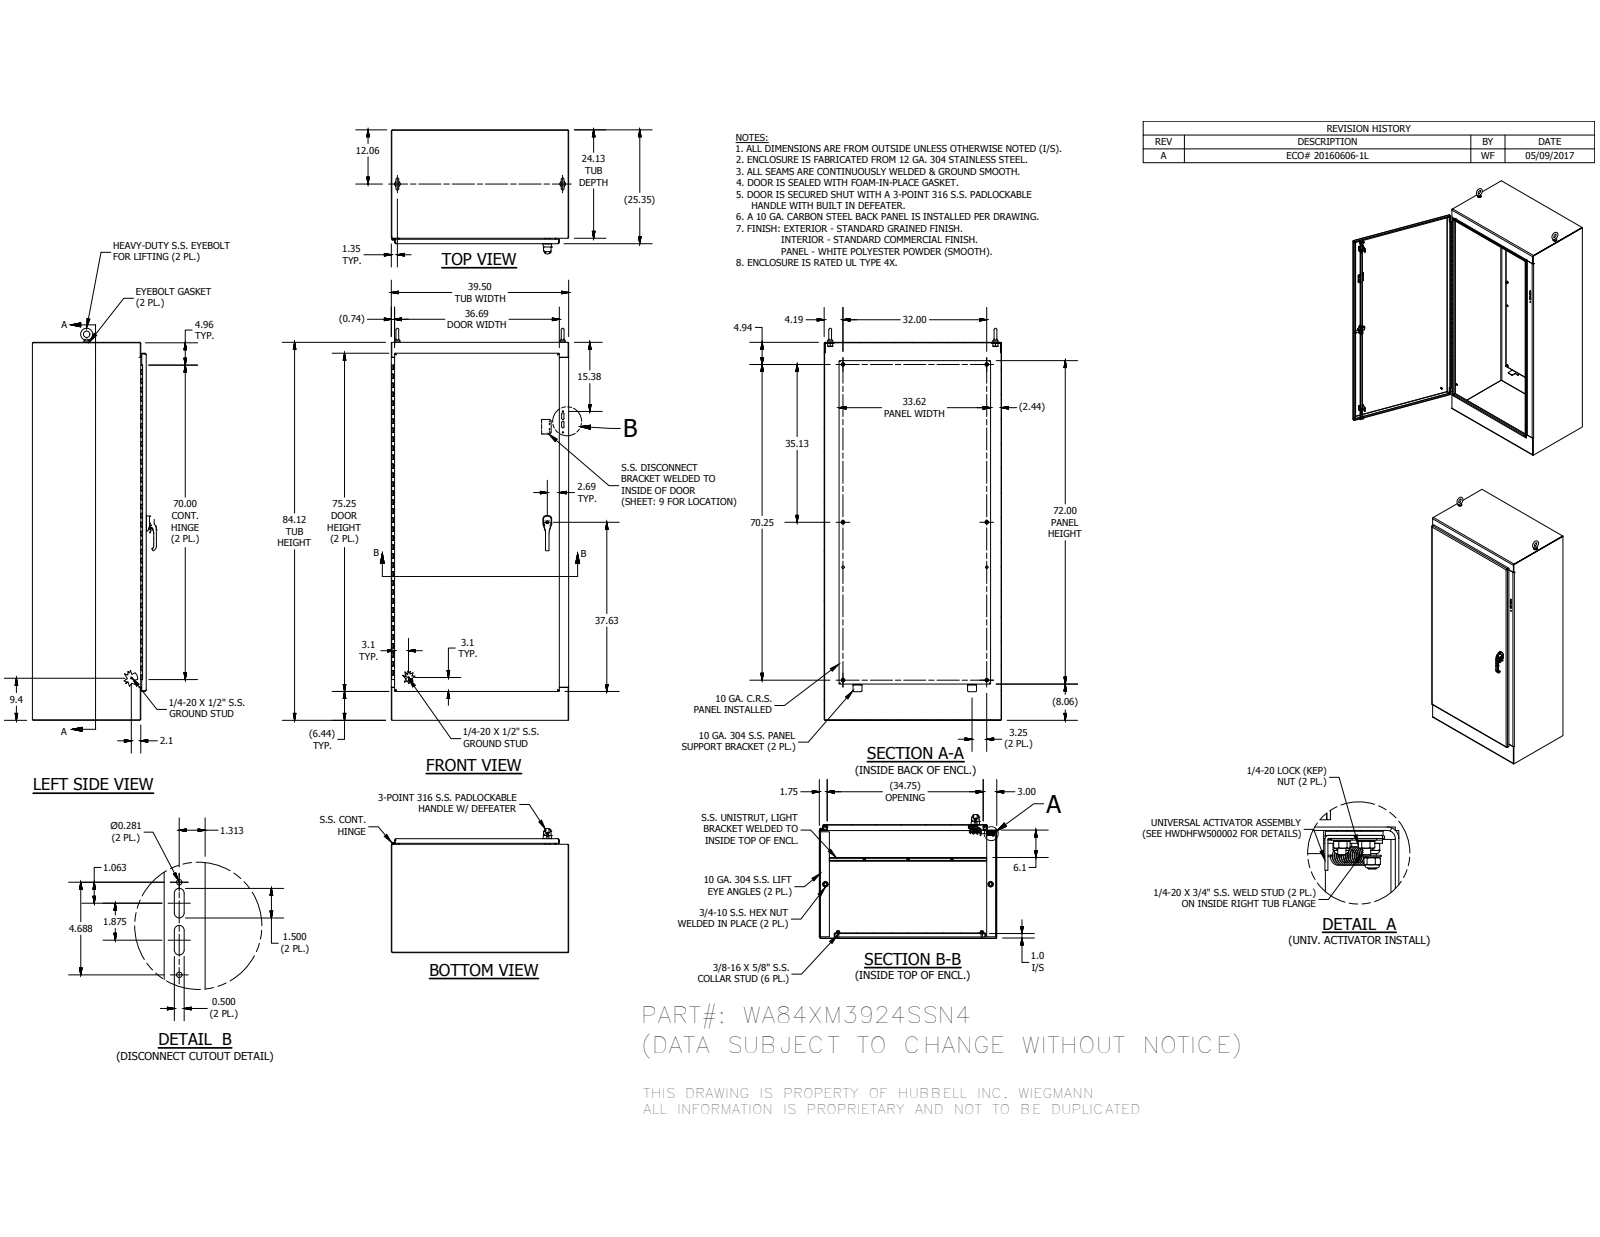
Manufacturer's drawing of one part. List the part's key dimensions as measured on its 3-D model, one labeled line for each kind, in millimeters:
Part name (STEP PRODUCT): WA84XM3924SSN4BLS; WAXM3924SSN4TOP; WAXM3924SSN4BTM; FUN00129_WAXM39SSN4 (+8 more)
STEP written by: Autodesk Inventor 2016 (AUTOMOTIVE_DESIGN)
Units: millimetres
Bodies: 127 solids, 4841 faces (2251 planar, 1548 cylindrical, 1042 other)
Overall size (bounding box): 2216.09 × 1003.3 × 700.95
Volume: 30 380 000 mm³ · Surface area: 21 680 000 mm²
Round holes (diameter × count): ⌀3.55 ×24, ⌀9.52 ×10, ⌀6.35 ×9, ⌀6.65 ×8, ⌀14.29 ×8, ⌀3.96 ×6, ⌀7.8 ×6, ⌀4.76 ×5, ⌀3.45 ×4, ⌀4.17 ×4, ⌀5.1 ×4, ⌀7.37 ×4
Round bosses / shafts (diameter × count): ⌀15.88 ×10, ⌀8.38 ×9, ⌀14.29 ×6, ⌀13.54 ×4, ⌀8.56 ×4, ⌀6.35 ×4, ⌀6.02 ×4, ⌀6 ×3
Partial cylindrical surfaces — rounded edges, fillets, slot ends (radius × count): R0.5 ×187, R0.3 ×109, R0.51 ×48, R6.35 ×25, R0.47 ×21, R1.59 ×20, R3.17 ×18, R0.64 ×16
Main face-to-face distances: 2.64, 641.19, 1000.66, 638.55, 643.83, 3.41, 25.4, 615.79, 31.45, 28.81
Hole centre spacings: 0.45, 395.11, 0.6, 1680.36, 9.65, 19.31, 197.56, 790.22
